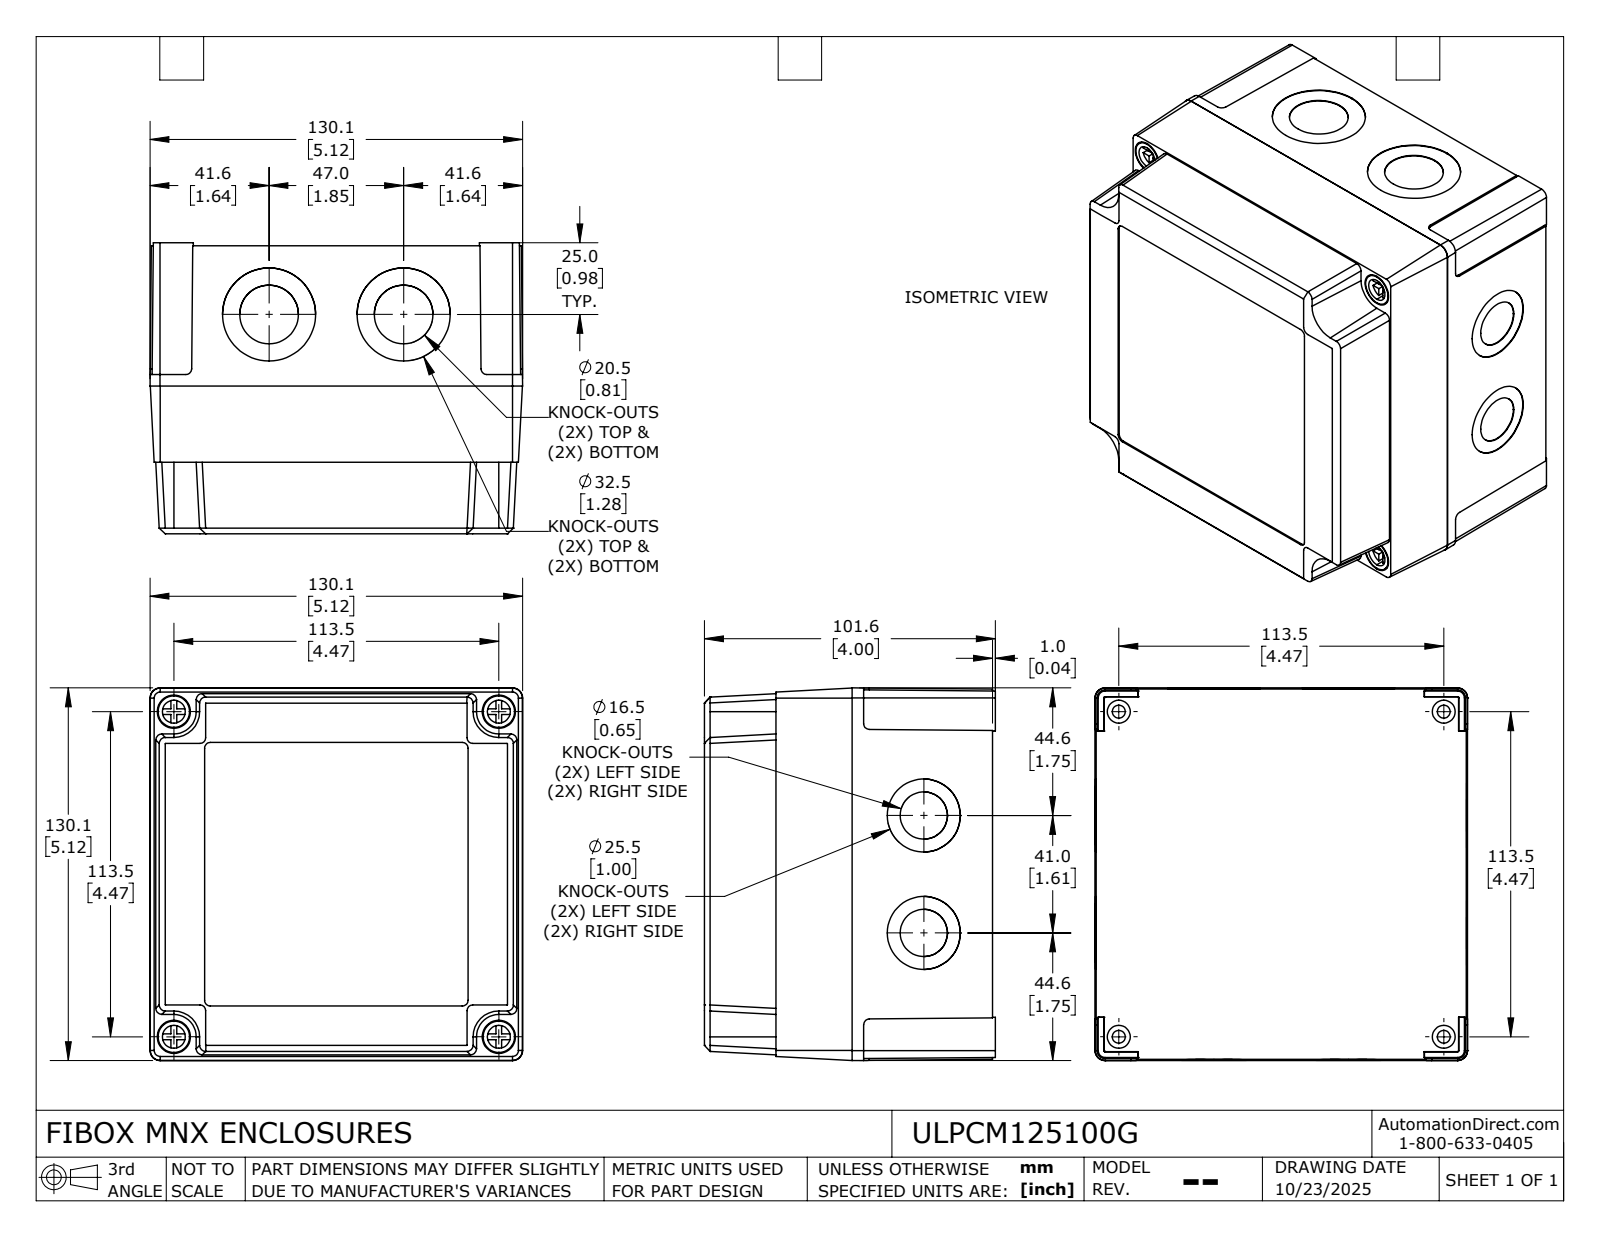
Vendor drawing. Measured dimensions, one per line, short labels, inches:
name: ULPCM125100G_Default
written by: SolidWorks 2024 (CONFIG_CONTROL_DESIGN)
unit: in
bodies: 6 solids, 569 faces (331 planar, 192 cylindrical, 46 other)
size: 5.122 × 5.122 × 4
volume: 16.19 in³; area: 274.1 in²
holes: 8× ⌀0.126, 8× ⌀0.157, 4× ⌀0.177, 4× ⌀0.315, 4× ⌀0.457, 4× ⌀0.65, 4× ⌀0.807, 4× ⌀1.004, 4× ⌀1.28
bosses: 8× ⌀0.315, 8× ⌀0.098, 4× ⌀0.433, 4× ⌀0.283
rounds: 8× R0.079, 8× R0.083, 6× R0.056, 4× R0.021, 4× R0.197, 2× R0.023
face distances: 0.165, 3.87, 0.118, 3.752, 0.078, 0.055, 0.022, 3.941, 3.823, 0.071
hole spacings: 2.281, 4.587, 0.888, 1.476, 1.796, 2.506, 3.543, 3.7
